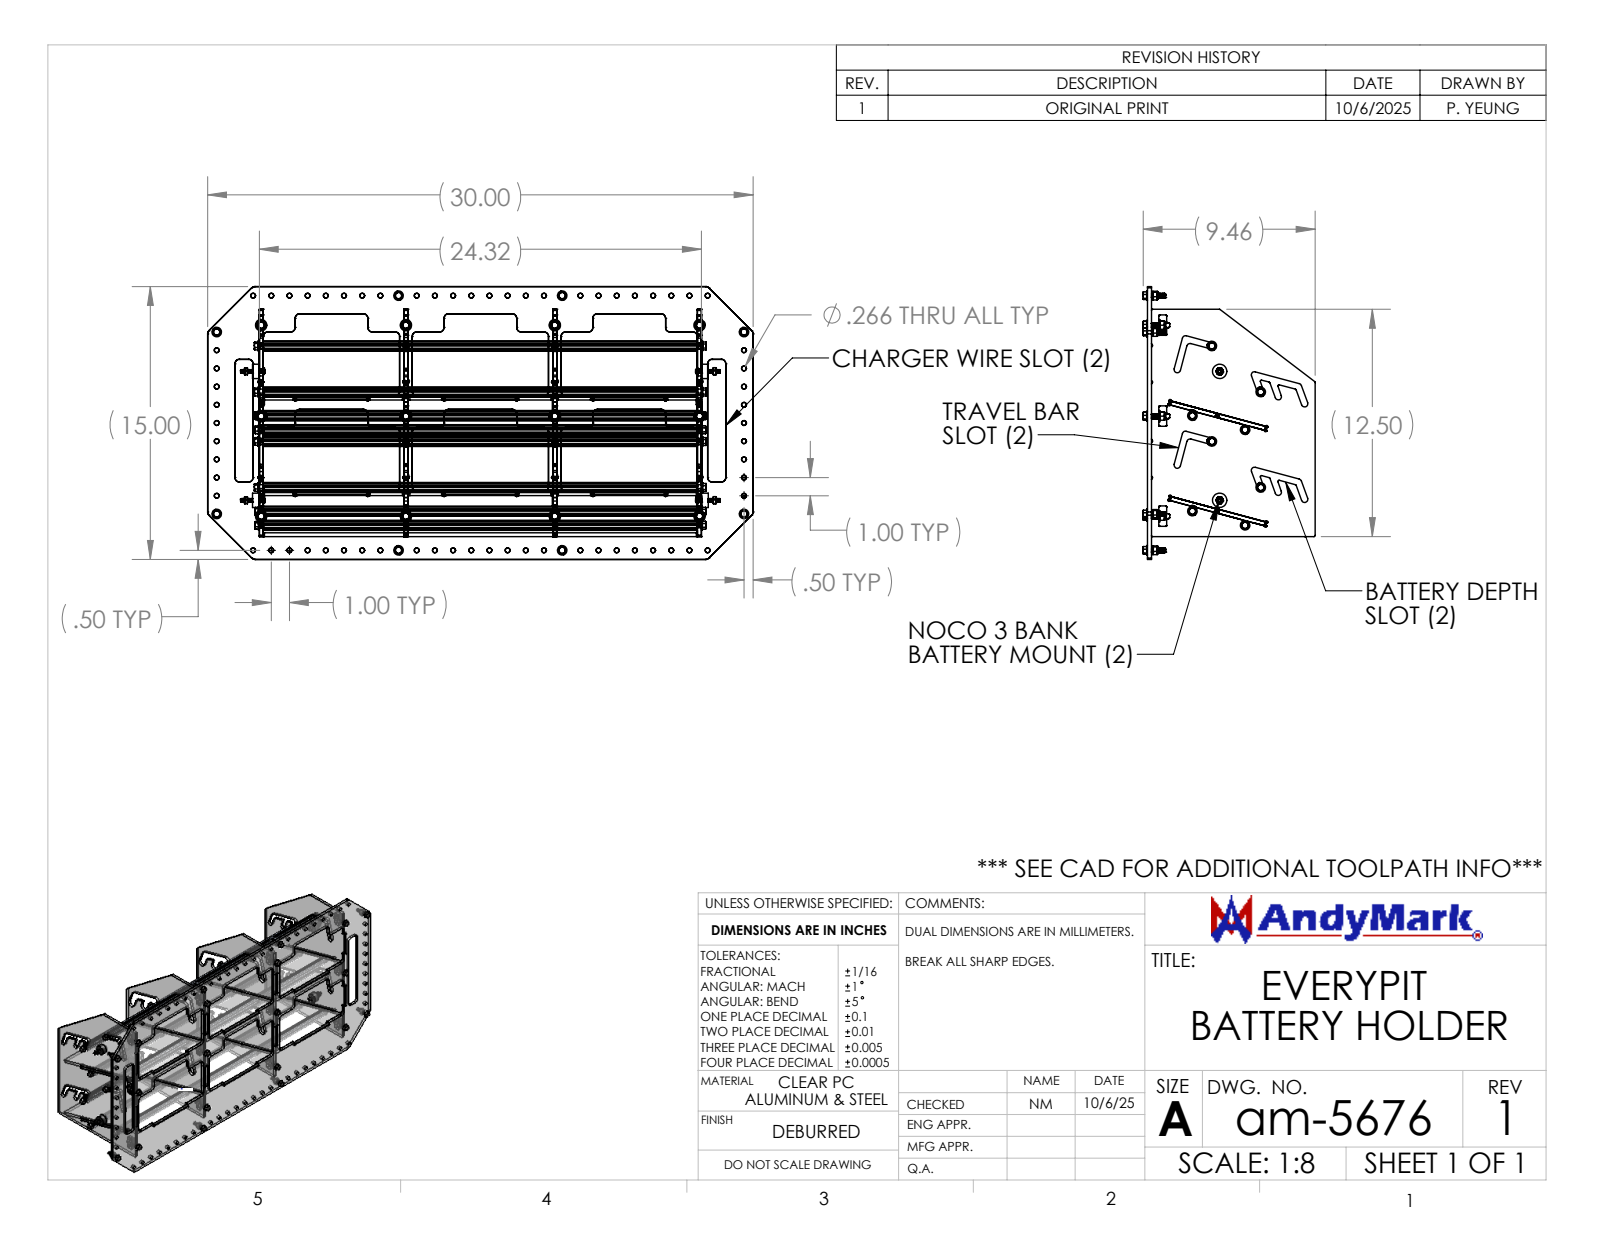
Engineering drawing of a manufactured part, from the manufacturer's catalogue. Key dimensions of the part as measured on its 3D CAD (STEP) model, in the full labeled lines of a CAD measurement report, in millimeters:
Part name (STEP PRODUCT): am-1260 10-32 x 1250 BHCS_am-1260 10-32 x 1250 BHCS; am-5676 EveryPit Battery Holder; am-4535-375 5mm Hex x 375IN Spacer; am-5676_faceplate EveryPit Face Plate (+8 more)
STEP written by: SolidWorks 2024 (AUTOMOTIVE_DESIGN)
Units: millimetres
Bodies: 127 solids, 21668 faces (2792 planar, 6984 cylindrical, 11892 other)
Overall size (bounding box): 762 × 381 × 240.3
Volume: 4 133 000 mm³ · Surface area: 1 875 000 mm²
Round holes (diameter × count): ⌀6.8 ×90, ⌀5.4 ×80, ⌀8.6 ×28, ⌀5.2 ×20, ⌀6.4 ×20, ⌀6.8 ×20, ⌀4.2 ×16, ⌀7.1 ×12, ⌀5.9 ×8, ⌀6.5 ×4, ⌀4.1 ×2, ⌀5.1 ×2
Round bosses / shafts (diameter × count): ⌀13.2 ×28, ⌀15.9 ×12, ⌀8 ×4, ⌀20 ×2, ⌀4.8 ×2
Partial cylindrical surfaces — rounded edges, fillets, slot ends (radius × count): R2.3 ×172, R0.7 ×108, R1.3 ×108, R3.1 ×108, R3.7 ×108, R1.6 ×90, R1.7 ×80, R6.4 ×64
Main face-to-face distances: 5.6, 128.8, 202, 410, 134.4, 123.2, 612, 207.6, 415.6, 196.4
Hole centre spacings: 0.5, 25.4, 50.8, 180, 76.2, 0.8, 359.2, 127
